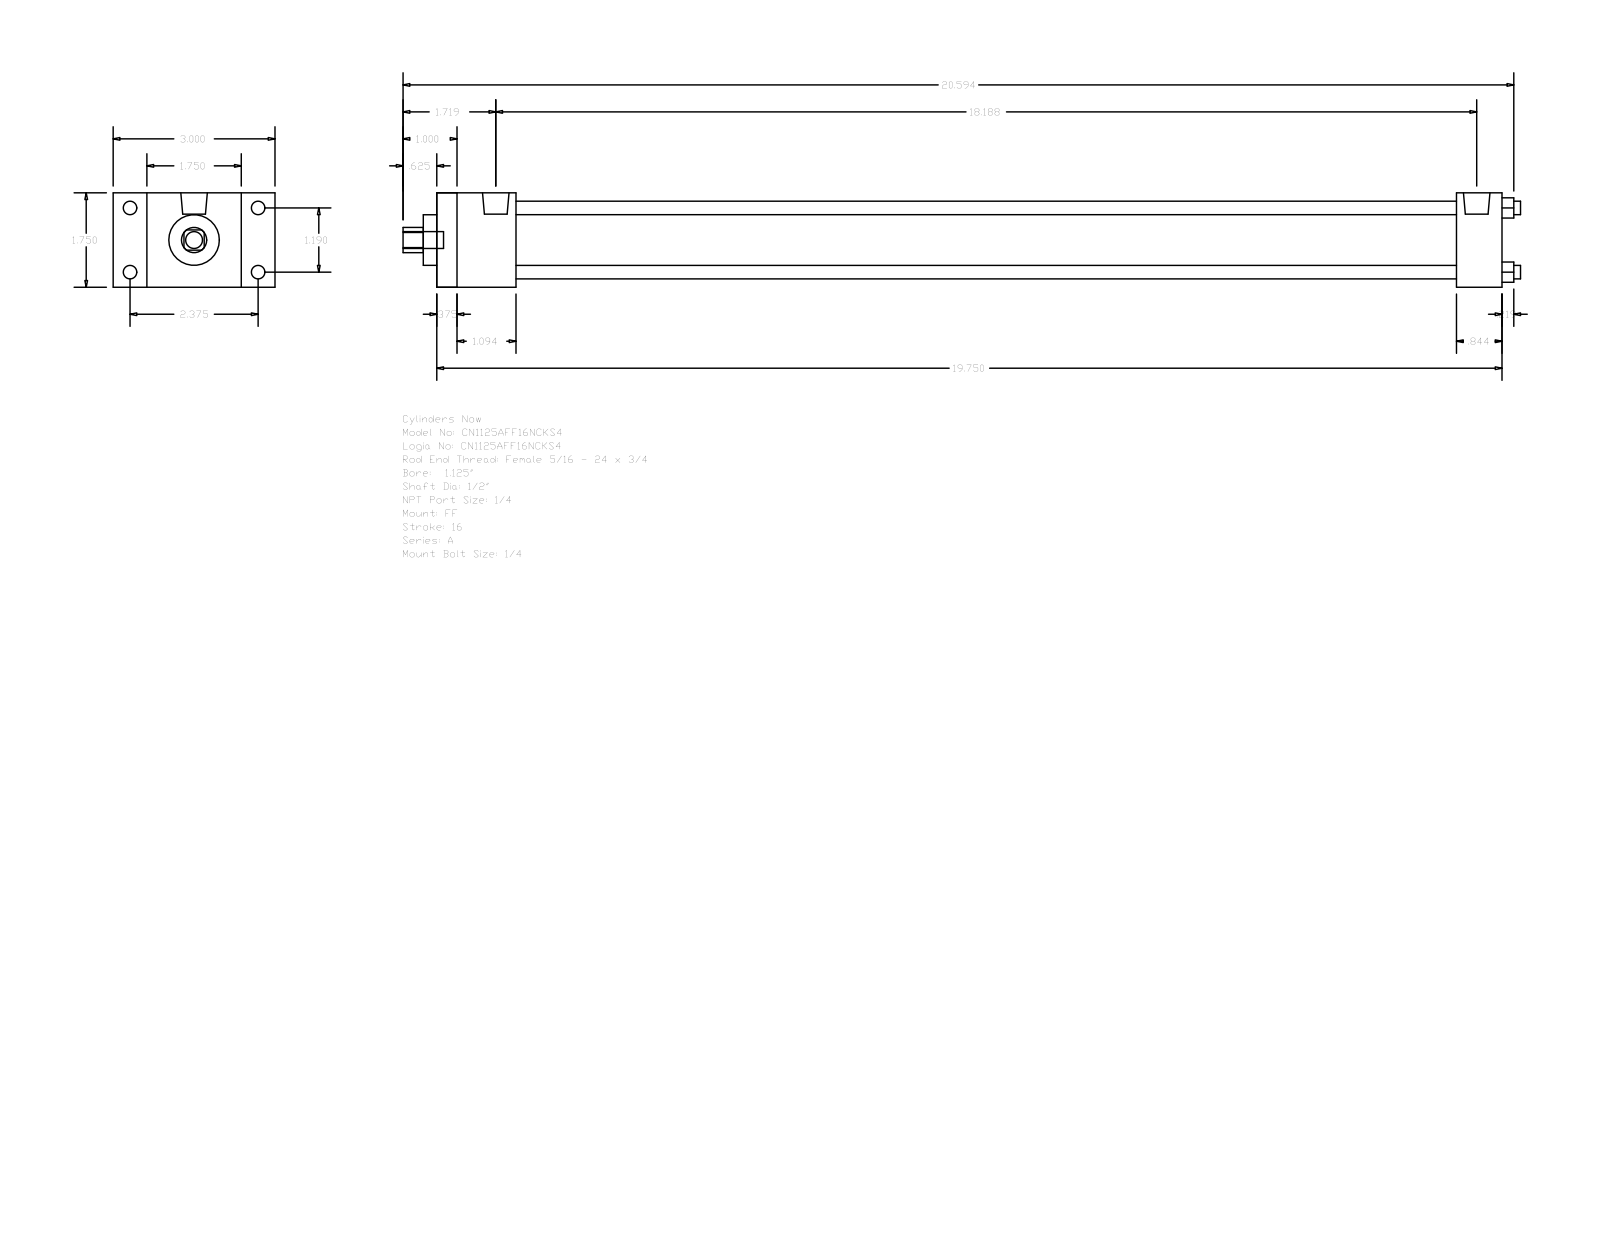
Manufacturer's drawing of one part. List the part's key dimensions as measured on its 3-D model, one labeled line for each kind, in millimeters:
Part name (STEP PRODUCT): A_FF__0112_0.5
STEP written by: GSSL Pune (CONFIG_CONTROL_DESIGN)
Units: millimetres
Bodies: 0 solids, 92 faces (64 planar, 28 cylindrical, 0 other)
Overall size (bounding box): 526.26 × 76.2 × 44.45
Round holes (diameter × count): ⌀6.35 ×4, ⌀12.7 ×1, ⌀23.81 ×1, ⌀31.88 ×1
Round bosses / shafts (diameter × count): ⌀6.35 ×4, ⌀5.56 ×4, ⌀12.49 ×2, ⌀7.94 ×1
Partial cylindrical surfaces — rounded edges, fillets, slot ends (radius × count): R5.94 ×1
Main face-to-face distances: 44.46, 501.64, 9.52, 492.12, 15.87, 480.21, 470.69, 21.43, 37.3, 27.78
Hole centre spacings: 21.37, 30.22, 42.74
